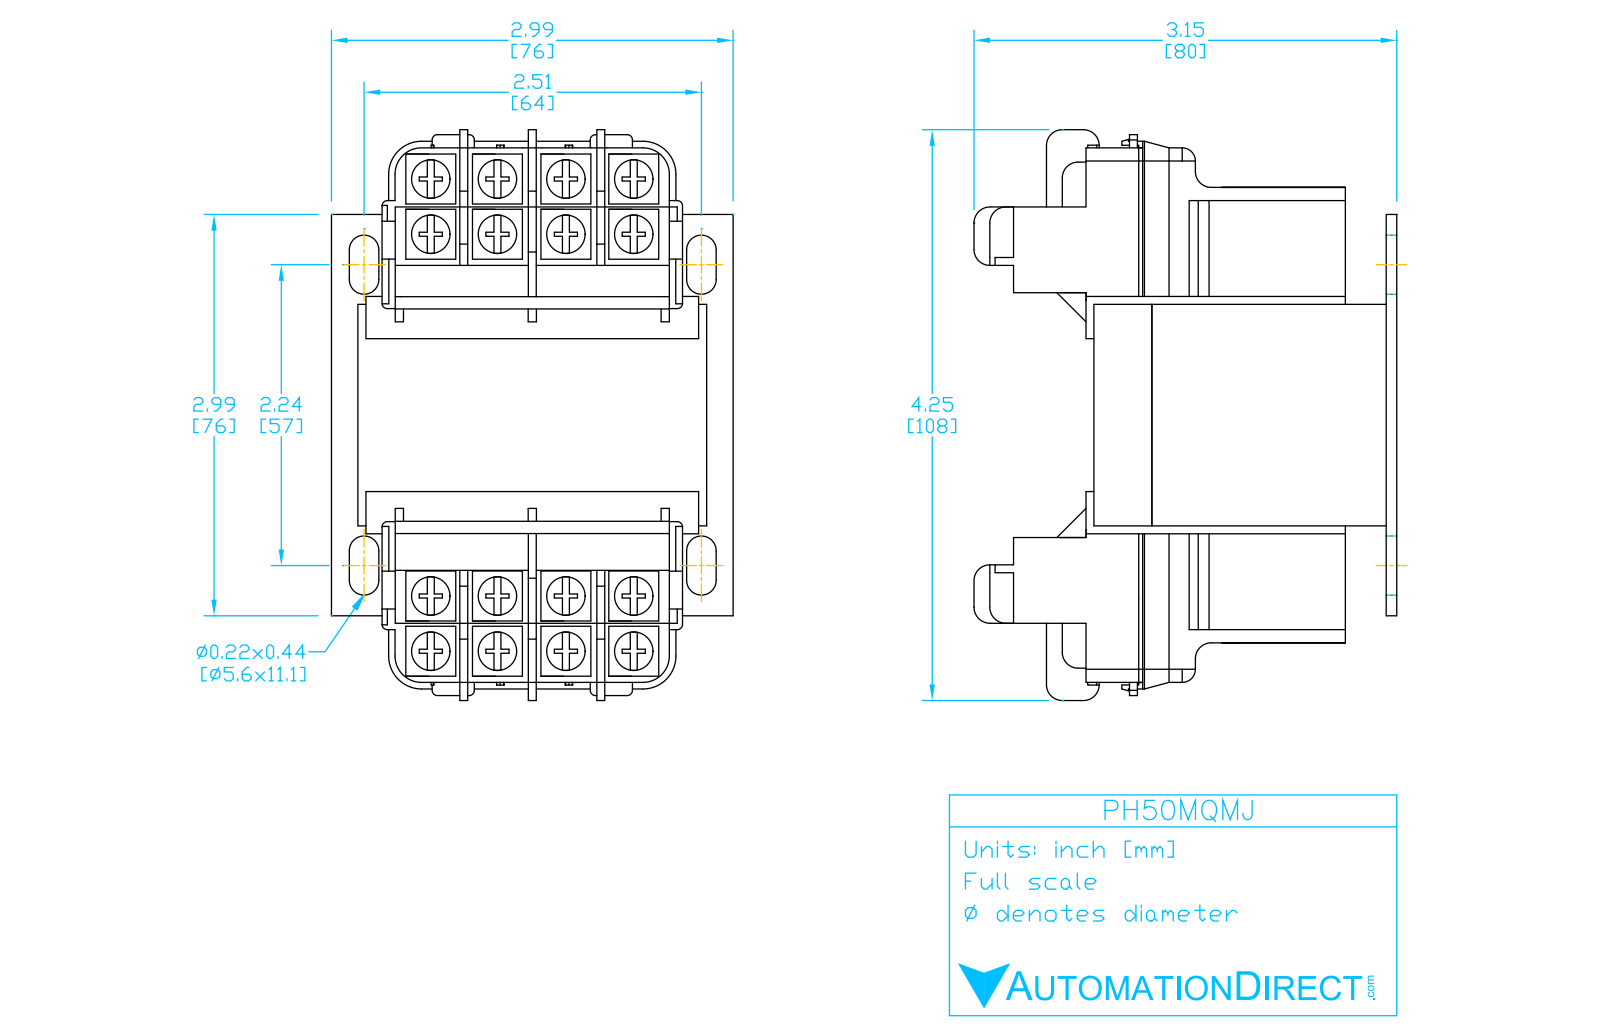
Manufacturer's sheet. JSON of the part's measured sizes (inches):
{"part_name": "PH50MQMJ", "step_written_by": "SolidWorks 2017 (AUTOMOTIVE_DESIGN)", "units": "inches", "bodies": {"solids": 8, "faces": 462, "planar": 336, "cylindrical": 114, "other": 12}, "overall_size": [4.213, 3.14, 3], "volume_in3": 16.06, "surface_area_in2": 112.9, "round_holes": [[0.157, 4]], "partial_cylinders_radius": [[0.039, 40], [0.089, 12], [0.11, 8], [0.05, 4], [0.098, 4], [0.1, 4], [0.147, 4], [0.196, 4]], "face_to_face_distances": [0.05, 1.654, 1.732, 0.059, 0.737, 2.441, 1.704, 1.801, 0.069, 0.433], "hole_center_spacings": [0.913, 2.313, 2.487]}
